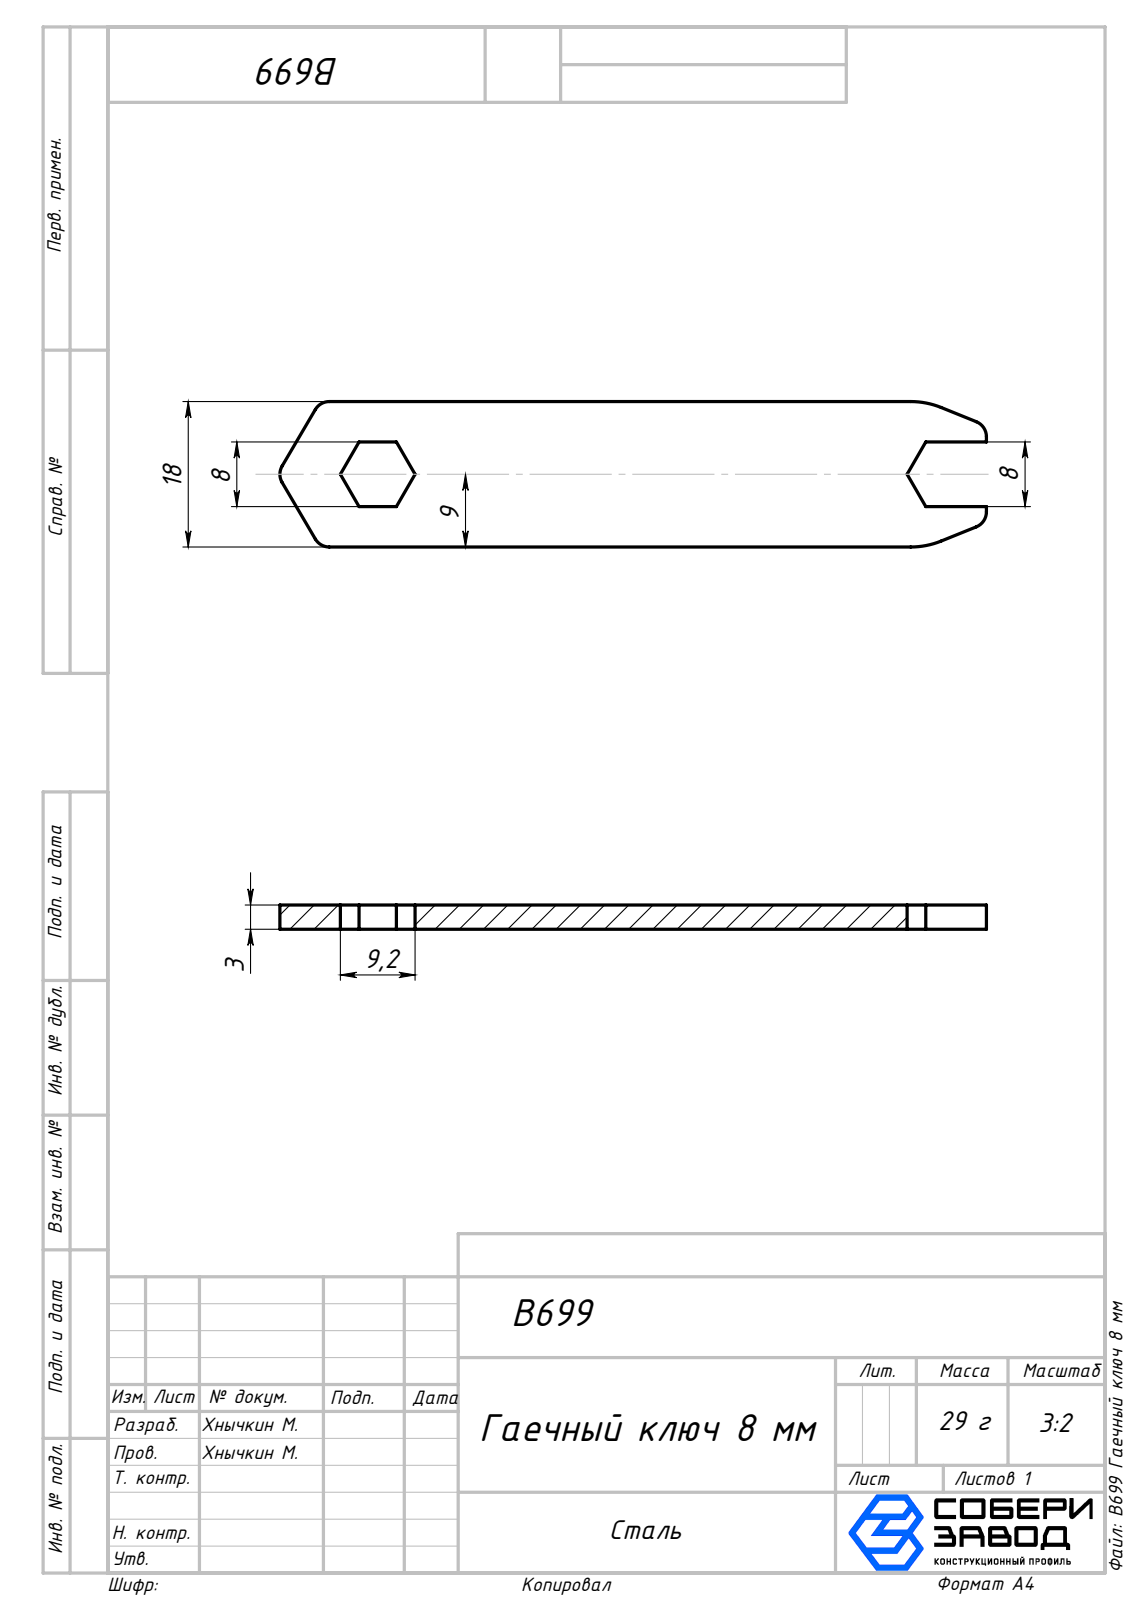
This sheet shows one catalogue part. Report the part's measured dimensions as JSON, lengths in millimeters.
{"part_name": "B699 Гаечный ключ 8 мм", "step_written_by": "SolidWorks 2025 (AUTOMOTIVE_DESIGN)", "units": "millimeters", "bodies": {"solids": 1, "faces": 27, "planar": 20, "cylindrical": 7, "other": 0}, "overall_size": [87.38, 18, 3], "volume_mm3": 4147, "surface_area_mm2": 3489, "partial_cylinders_radius": [[2, 5], [10, 2]], "face_to_face_distances": [3, 18, 5, 13, 8, 60.7, 52.7]}
